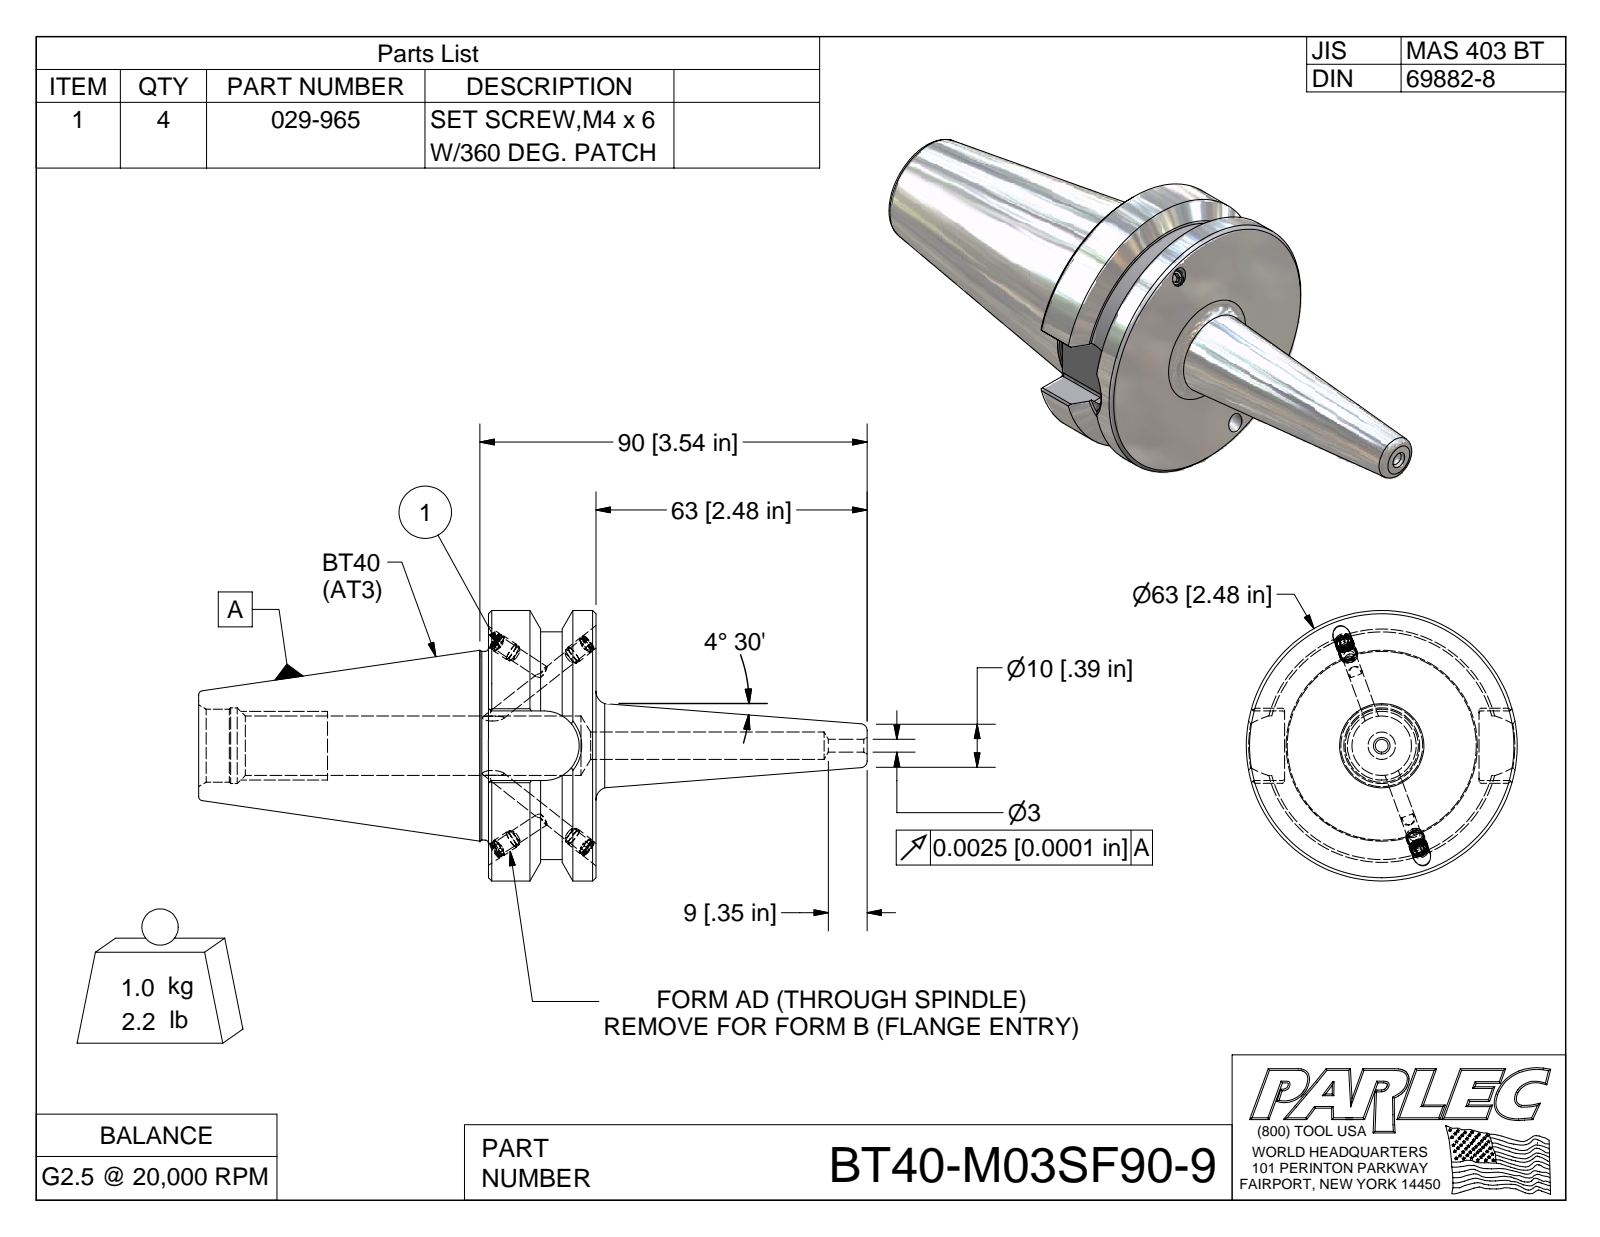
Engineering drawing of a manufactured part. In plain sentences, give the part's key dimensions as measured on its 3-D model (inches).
The part is named "BT40-M03SF90-9; BT40BC-M03SF90-9-1; 029-965". Its 3-D file was written by "Autodesk Inventor 2009 (AUTOMOTIVE_DESIGN)". It is 5 solids with 149 faces: 67 planar, 39 cylindrical and 43 other. Overall it measures 6.118 by 2.48 by 2.48 inches. Its volume is 7.866 cubic inches and its surface area 42.78 square inches. Round holes: 4 of diameter 0.13, 4 of diameter 0.161, 1 of diameter 0.118, 1 of diameter 0.694. Round bosses or shafts: 4 of diameter 0.165, 4 of diameter 0.157, 1 of diameter 2.48, 1 of diameter 2.087, 1 of diameter 1.75, 1 of diameter 1.73. Partial cylindrical surfaces (rounded edges, fillets, slot ends): 8 of radius 0.02, 1 of radius 0.319. The main face-to-face distances are 0.984, 1.78, 2.653, 3.637, 0.637, 3.328, 0.675, 0.309, 3.131, 0.478.
